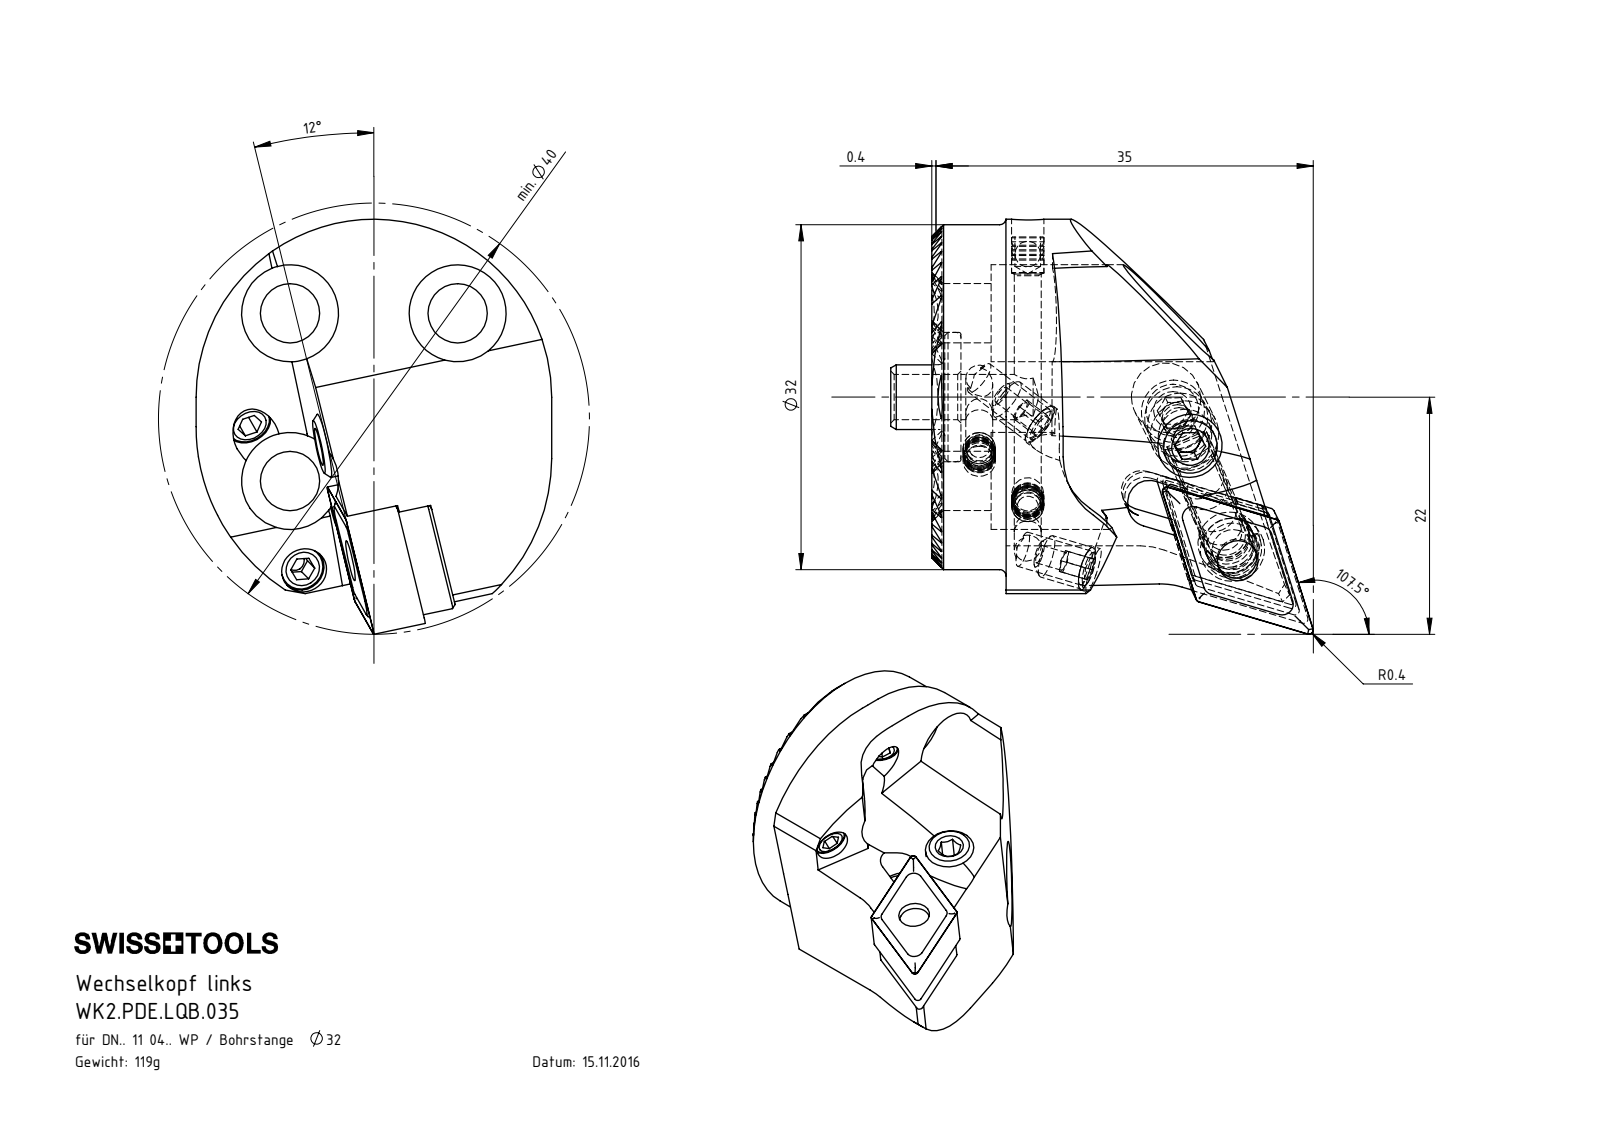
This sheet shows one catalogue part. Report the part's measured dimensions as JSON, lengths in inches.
{"part_name": "WDE-ER4.101.017_A; WDE-ER1.101.000; WKX-ER1.004.005_A_PreviewCfg; WK2-PDE.LQB.035_A (+6 more)", "step_written_by": "SolidWorks 2017 (AUTOMOTIVE_DESIGN)", "units": "inches", "bodies": {"solids": 15, "faces": 477, "planar": 256, "cylindrical": 111, "other": 110}, "overall_size": [1.544, 1.516, 1.299], "volume_in3": 0.951, "surface_area_in2": 15.02, "round_holes": [[0.094, 3], [0.098, 3], [0.165, 3], [0.217, 3], [0.354, 3], [0.067, 2], [0.118, 2], [0.13, 2], [0.15, 1], [0.189, 1], [0.197, 1], [0.252, 1]], "round_bosses_or_shafts": [[0.118, 3], [0.236, 2], [0.157, 2], [1.26, 1], [0.232, 1], [0.113, 1]], "partial_cylinders_radius": [[0.005, 22], [0.016, 8], [0.083, 5], [0.276, 2], [0.072, 1], [0.073, 1], [0.089, 1], [0.093, 1]], "face_to_face_distances": [0.051, 0.102, 0.154, 0.205, 0.307, 0.256, 0.511, 0.46, 0.563, 0.409], "hole_center_spacings": [0.433, 0.613, 0.465, 0.867]}
